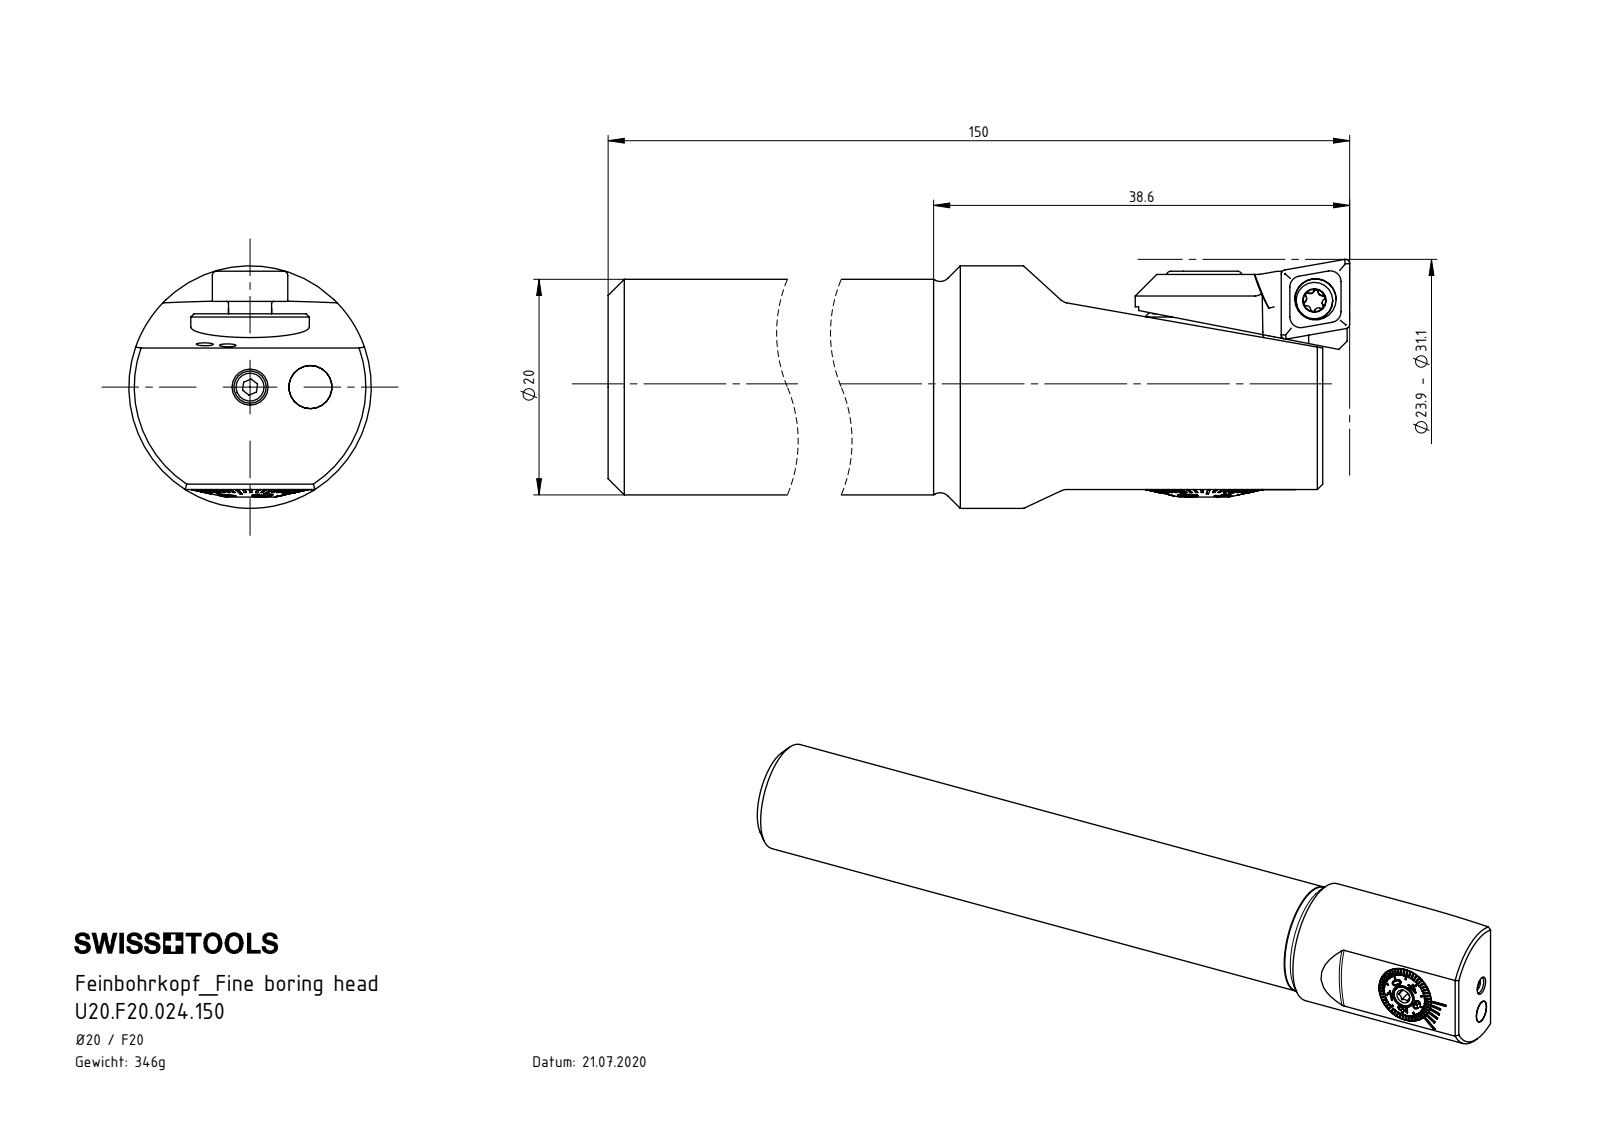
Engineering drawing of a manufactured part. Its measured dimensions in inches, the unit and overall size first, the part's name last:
Units: inches
Overall size (bounding box): 5.807 × 0.886 × 0.886
Round holes (diameter × count): ⌀0.083 ×4, ⌀0.059 ×2, ⌀0.118 ×2, ⌀0.13 ×2, ⌀0.043 ×1, ⌀0.075 ×1, ⌀0.157 ×1, ⌀0.177 ×1, ⌀0.197 ×1, ⌀0.213 ×1, ⌀0.244 ×1, ⌀0.256 ×1
Round bosses / shafts (diameter × count): ⌀0.157 ×2, ⌀0.156 ×2, ⌀0.886 ×1, ⌀0.787 ×1, ⌀0.433 ×1, ⌀0.432 ×1, ⌀0.427 ×1, ⌀0.341 ×1
Partial cylindrical surfaces — rounded edges, fillets, slot ends (radius × count): R0.012 ×2, R0.049 ×2, R0.079 ×2
Main face-to-face distances: 5.807, 0.146, 0.059, 0.031, 0.114, 0.11, 0.055, 0.496, 0.61, 0.642
Hole centre spacings: 0.212, 0.22, 0.343
Volume: 2.701 in³ · Surface area: 24.31 in²
Bodies: 13 solids, 496 faces (284 planar, 53 cylindrical, 159 other)
Part name (STEP PRODUCT): F20-BG1.AA4.011_verstellbar; U20.F20.AA4.150; F20-BG2.011.004_A; ISO 4762 - M1.4 x 6 (+8 more)
STEP written by: SolidWorks 2017 (AUTOMOTIVE_DESIGN)
